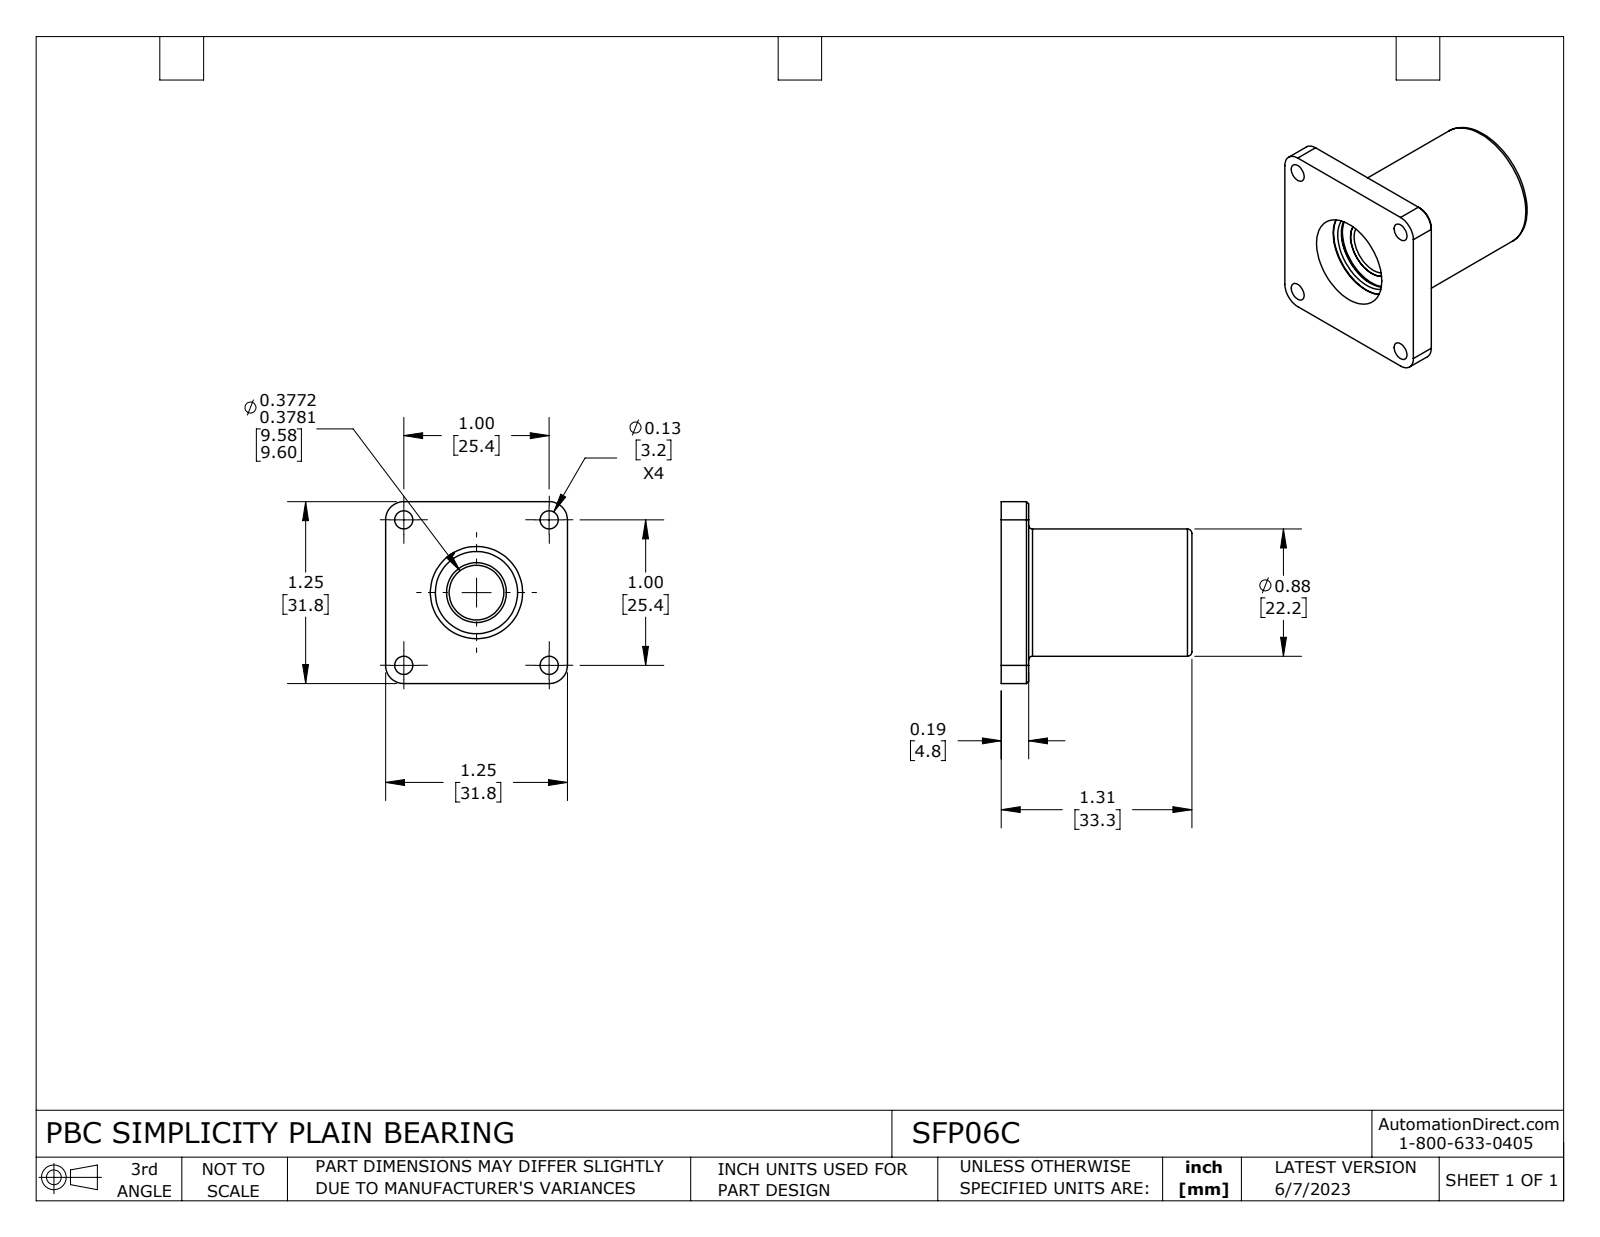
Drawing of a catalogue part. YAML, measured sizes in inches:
part_name: "SFP06C"
step_written_by: "SolidWorks 2021 (CONFIG_CONTROL_DESIGN)"
units: inches
bodies: {solids: 7, faces: 169, planar: 41, cylindrical: 74, other: 54}
overall_size: [1.31, 1.25, 1.25]
volume: 0.712
surface_area: 16.4
round_holes:
  - {diameter: 0.125, count: 4}
  - {diameter: 0.376, count: 1}
  - {diameter: 0.411, count: 1}
  - {diameter: 0.565, count: 1}
  - {diameter: 0.634, count: 1}
  - {diameter: 0.667, count: 1}
round_bosses_or_shafts:
  - {diameter: 0.875, count: 1}
  - {diameter: 0.675, count: 1}
  - {diameter: 0.624, count: 1}
  - {diameter: 0.587, count: 1}
  - {diameter: 0.524, count: 1}
partial_cylinders:
  - {radius: 0.009, count: 4}
  - {radius: 0.125, count: 4}
  - {radius: 0.004, count: 2}
  - {radius: 0.014, count: 2}
face_to_face_distances: [0.188, 1.25, 0.035, 0.931, 1.31, 1.122, 0.26, 0.34, 0.527, 0.607]
hole_center_spacings: [0.707, 1, 1.414]
